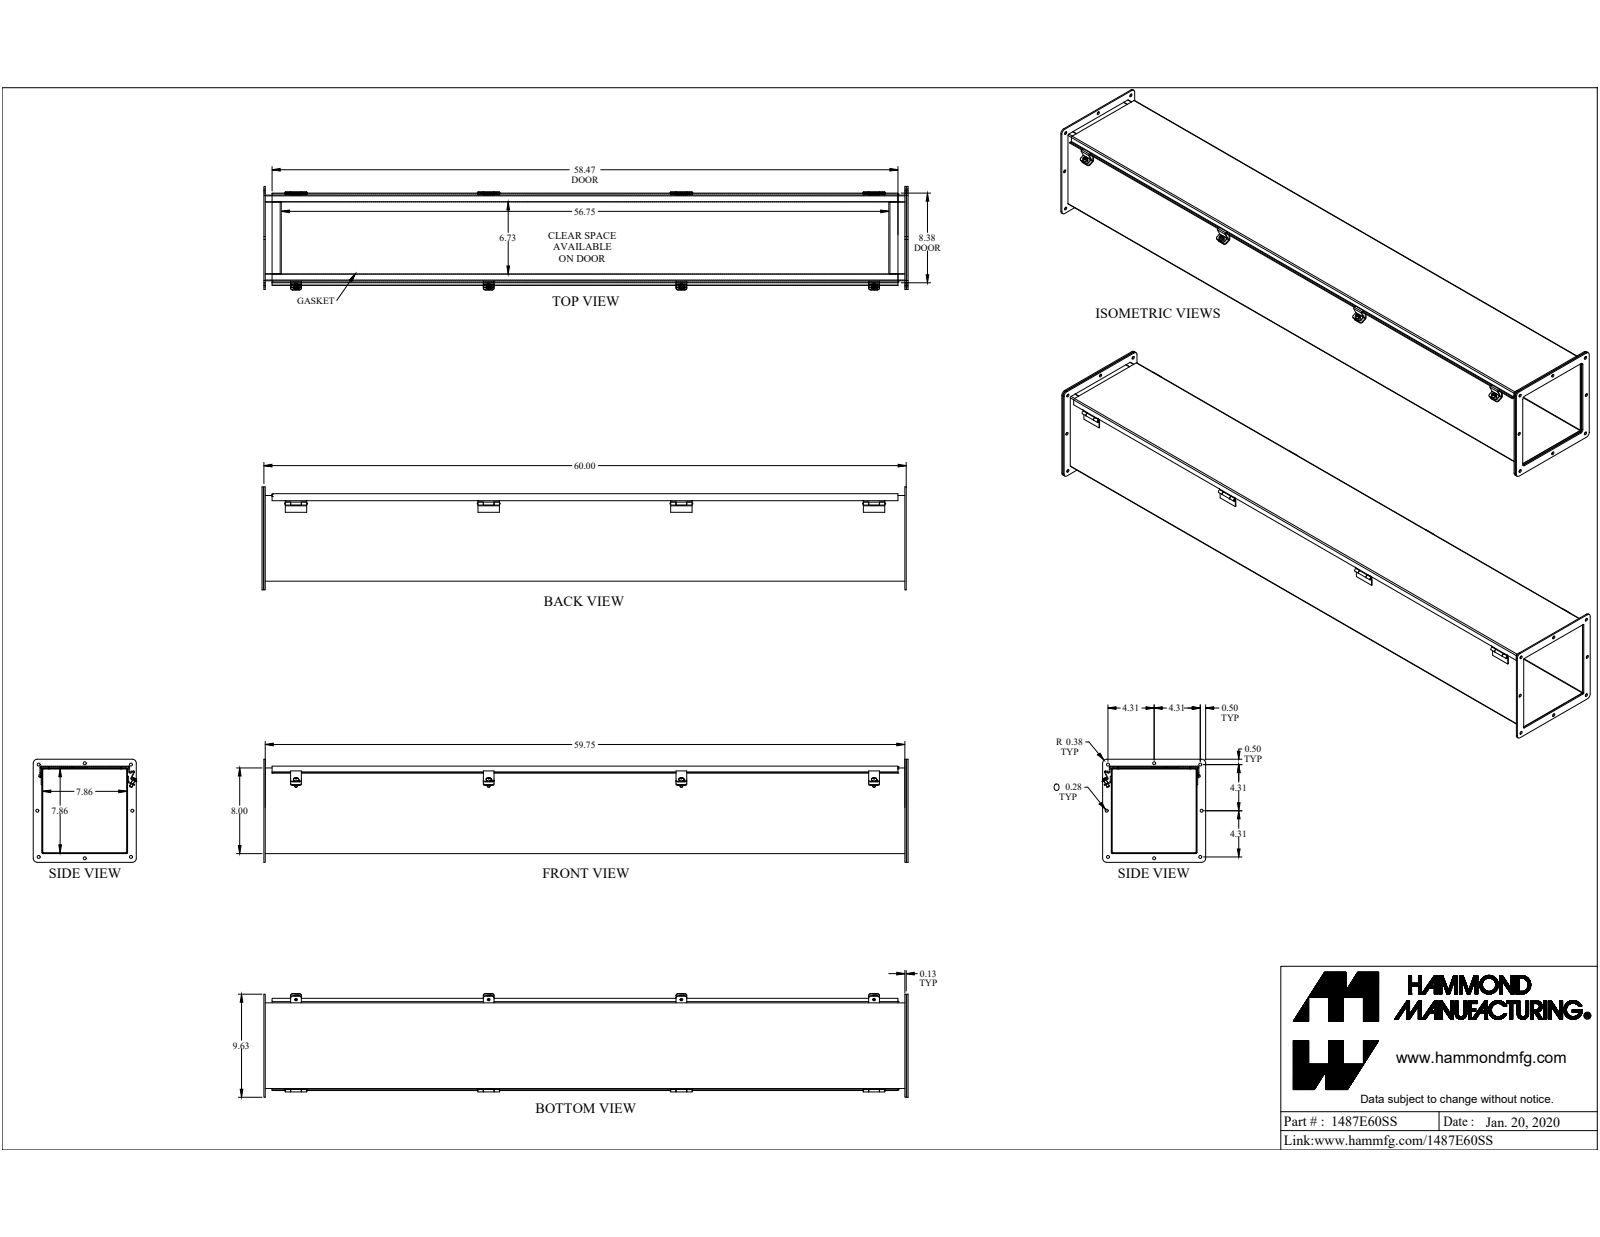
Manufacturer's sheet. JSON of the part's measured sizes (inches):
{"part_name": "1487E60SS", "step_written_by": "SolidWorks 2019 (CONFIG_CONTROL_DESIGN)", "units": "inches", "bodies": {"solids": 39, "faces": 794, "planar": 508, "cylindrical": 216, "other": 70}, "overall_size": [60.546, 9.677, 9.625], "volume_in3": 181.2, "surface_area_in2": 4708, "round_holes": [[0.281, 8], [0.213, 4], [0.187, 1], [0.196, 1], [0.258, 1], [0.35, 1]], "round_bosses_or_shafts": [[0.25, 5], [0.48, 4], [0.5, 1], [0.337, 1], [0.18, 1]], "partial_cylinders_radius": [[0.188, 16], [0.03, 8], [0.141, 8], [0.375, 8], [0.036, 7], [0.108, 7], [0.02, 6], [0.063, 4]], "face_to_face_distances": [0.072, 7.928, 8.1, 8, 7.856, 8.172, 8.028, 0.187, 0.172, 0.259], "hole_center_spacings": [4.315, 9.755, 6.276, 18, 4.314, 8.625, 8.625, 9.755]}
